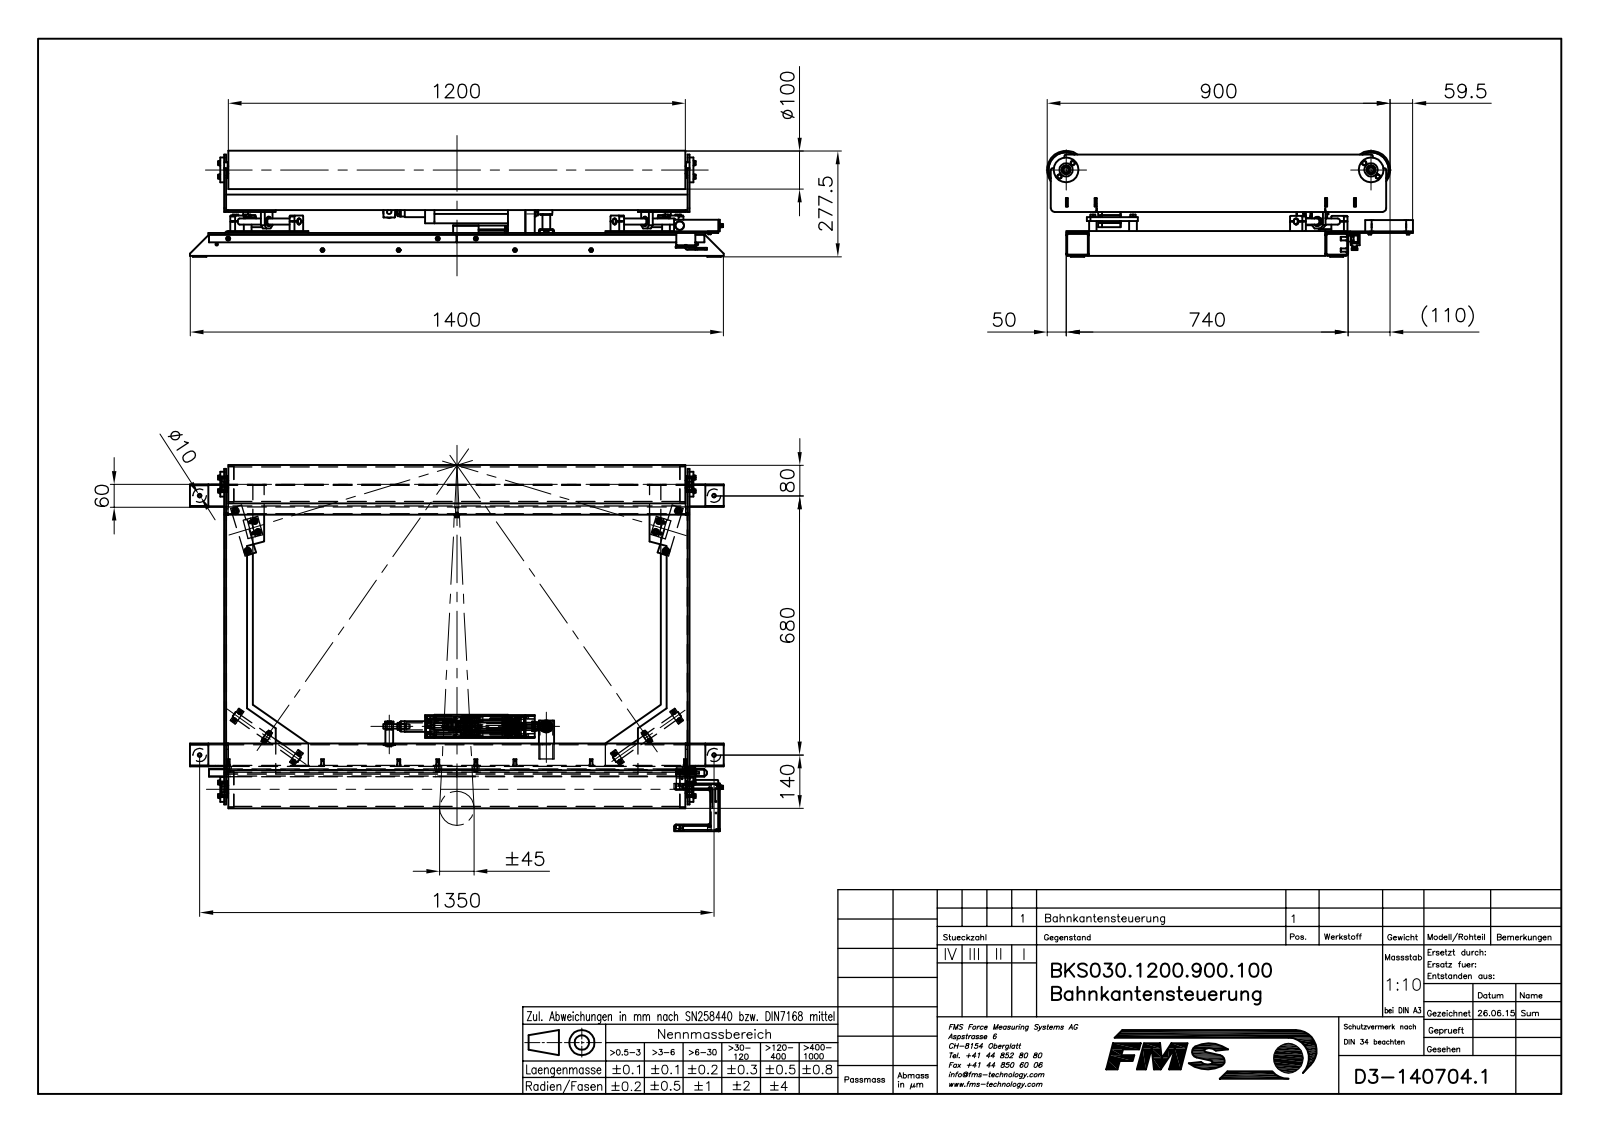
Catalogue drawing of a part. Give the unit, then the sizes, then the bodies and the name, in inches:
Units: inches
Overall size (bounding box): 55.118 × 37.776 × 10.925
Round holes (diameter × count): ⌀0.203 ×29, ⌀0.276 ×19, ⌀0.169 ×12, ⌀0.433 ×12, ⌀0.331 ×10, ⌀0.252 ×9, ⌀0.394 ×8, ⌀0.135 ×6, ⌀0.63 ×6, ⌀0.102 ×4, ⌀0.126 ×4, ⌀0.217 ×4
Round bosses / shafts (diameter × count): ⌀0.236 ×22, ⌀0.394 ×16, ⌀0.354 ×14, ⌀0.315 ×13, ⌀0.63 ×12, ⌀0.472 ×11, ⌀0.157 ×10, ⌀0.787 ×8
Partial cylindrical surfaces — rounded edges, fillets, slot ends (radius × count): R0.039 ×22, R0.079 ×19, R0.197 ×19, R0.157 ×16, R0.118 ×8, R0.236 ×8, R0.394 ×6, R0.016 ×4
Main face-to-face distances: 0.118, 0.197, 2.362, 2.244, 26.772, 1.457, 2.48, 3.937, 4.724, 6.181
Hole centre spacings: 1.181, 3.74, 0.945, 3.857, 0.984, 2.255, 7.874, 7.962
Volume: 688.3 in³ · Surface area: 8 674 in²
Bodies: 164 solids, 2768 faces (1313 planar, 1037 cylindrical, 418 other)
Part name (STEP PRODUCT): K1407041; K1407042; K1407044; K1407045 (+8 more)
STEP written by: Mechanical Desktop 2009 (CONFIG_CONTROL_DESIGN)
